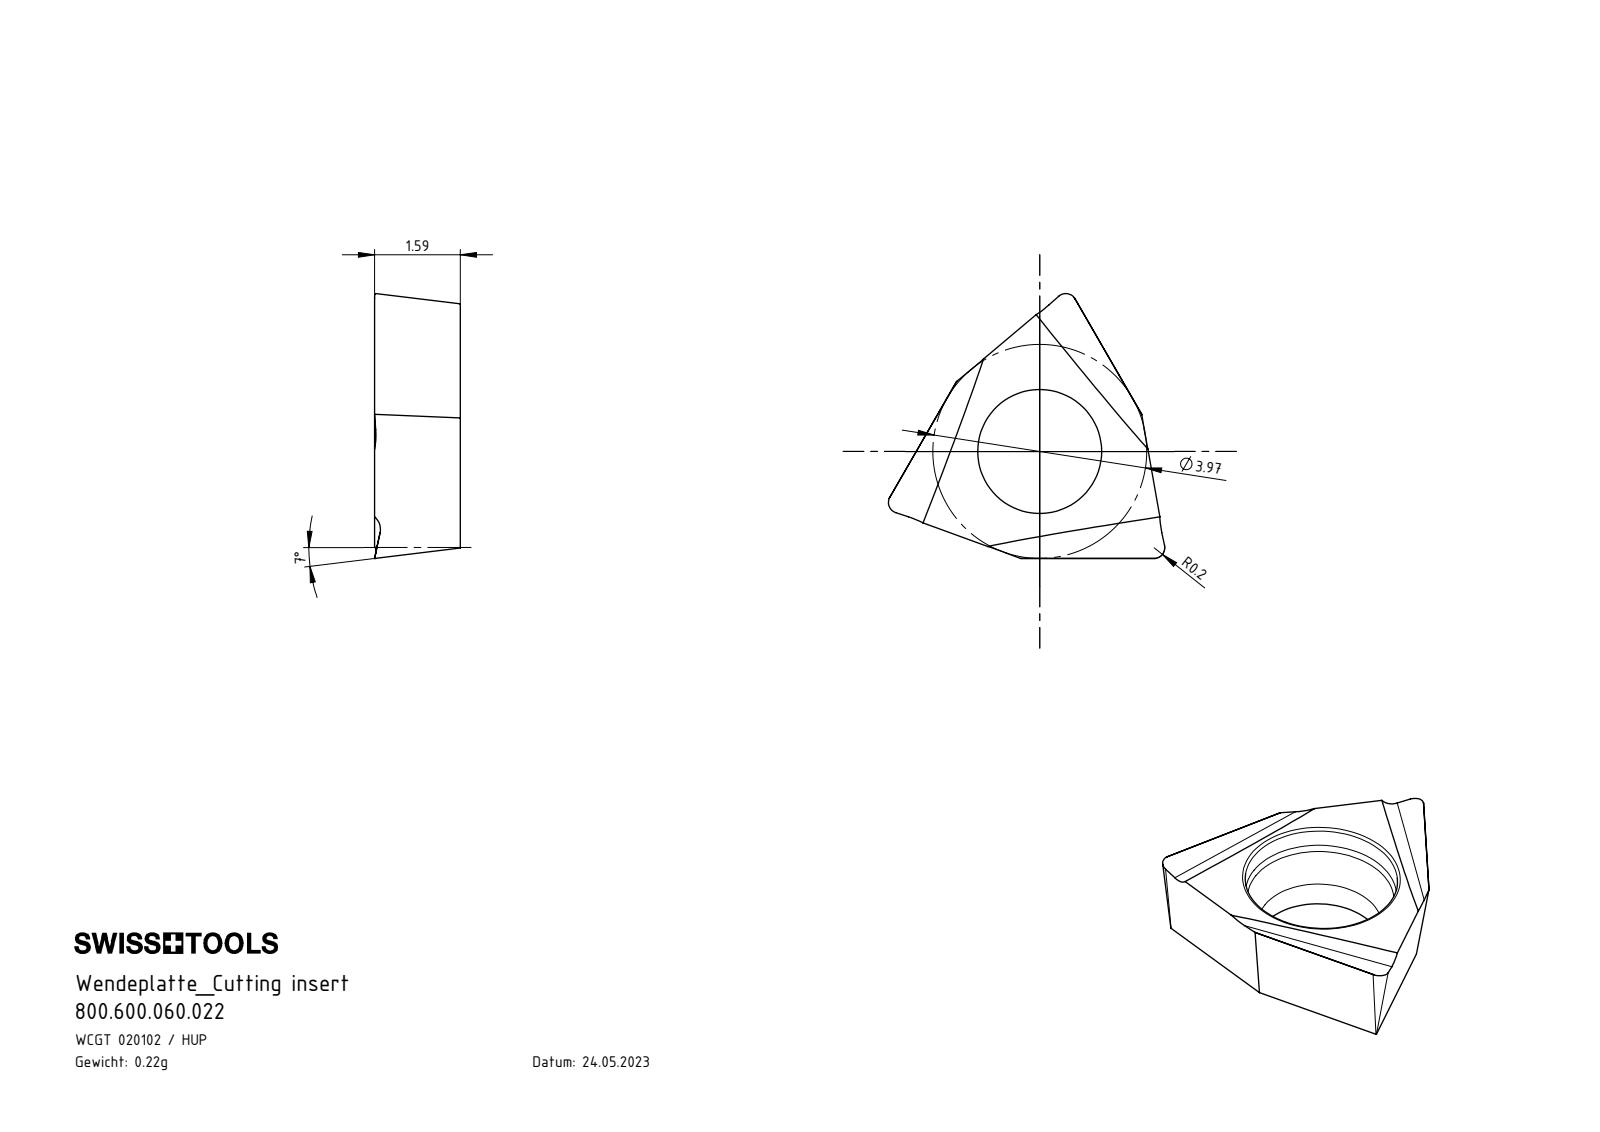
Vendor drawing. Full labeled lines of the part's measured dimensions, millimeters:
Part name (STEP PRODUCT): WWA.SFH.020.004
STEP written by: SolidWorks 2017 (AUTOMOTIVE_DESIGN)
Units: millimetres
Bodies: 1 solid, 31 faces (14 planar, 5 cylindrical, 12 other)
Overall size (bounding box): 5.13 × 4.92 × 1.59
Volume: 15 mm³ · Surface area: 56 mm²
Round holes (diameter × count): ⌀2.3 ×1
Partial cylindrical surfaces — rounded edges, fillets, slot ends (radius × count): R0.3 ×3
Main face-to-face distances: 1.59
